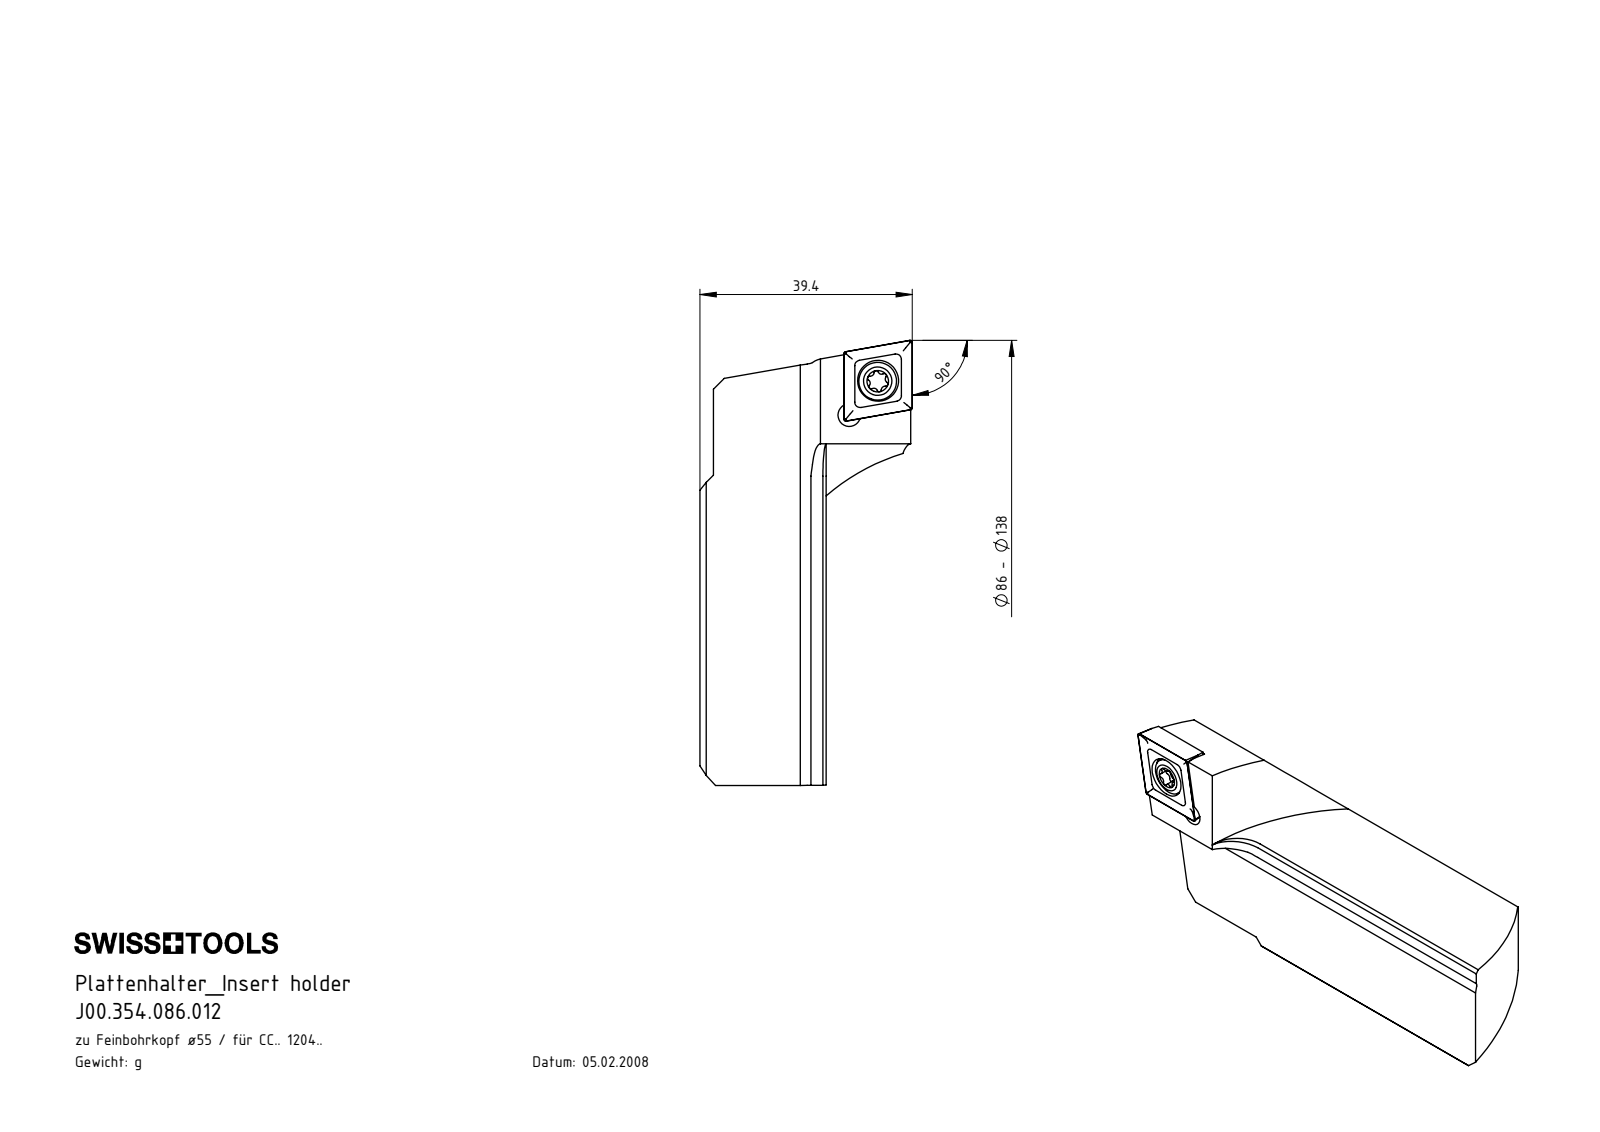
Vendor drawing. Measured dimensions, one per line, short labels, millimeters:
name: CCMT120404; J00.354.086.012; F00-WCC.086.001_C; WCC-ER2.001.010_A
written by: SolidWorks 2017 (CONFIG_CONTROL_DESIGN)
unit: mm
bodies: 3 solids, 379 faces (226 planar, 40 cylindrical, 113 other)
size: 82.58 × 39.4 × 27.35
volume: 33 749 mm³; area: 9 364 mm²
holes: 2× ⌀4.2, 1× ⌀5.5, 1× ⌀7.6
bosses: 1× ⌀7, 1× ⌀5
rounds: 8× R0.2, 6× R0.39, 3× R0.69, 3× R0.69, 3× R40, 1× R0.8, 1× R6
face distances: 2.38, 21.3, 4.76, 7.14, 9.52, 4.77, 7.15, 9.53, 11.91, 14.29
hole spacings: 8.21, 8.33
